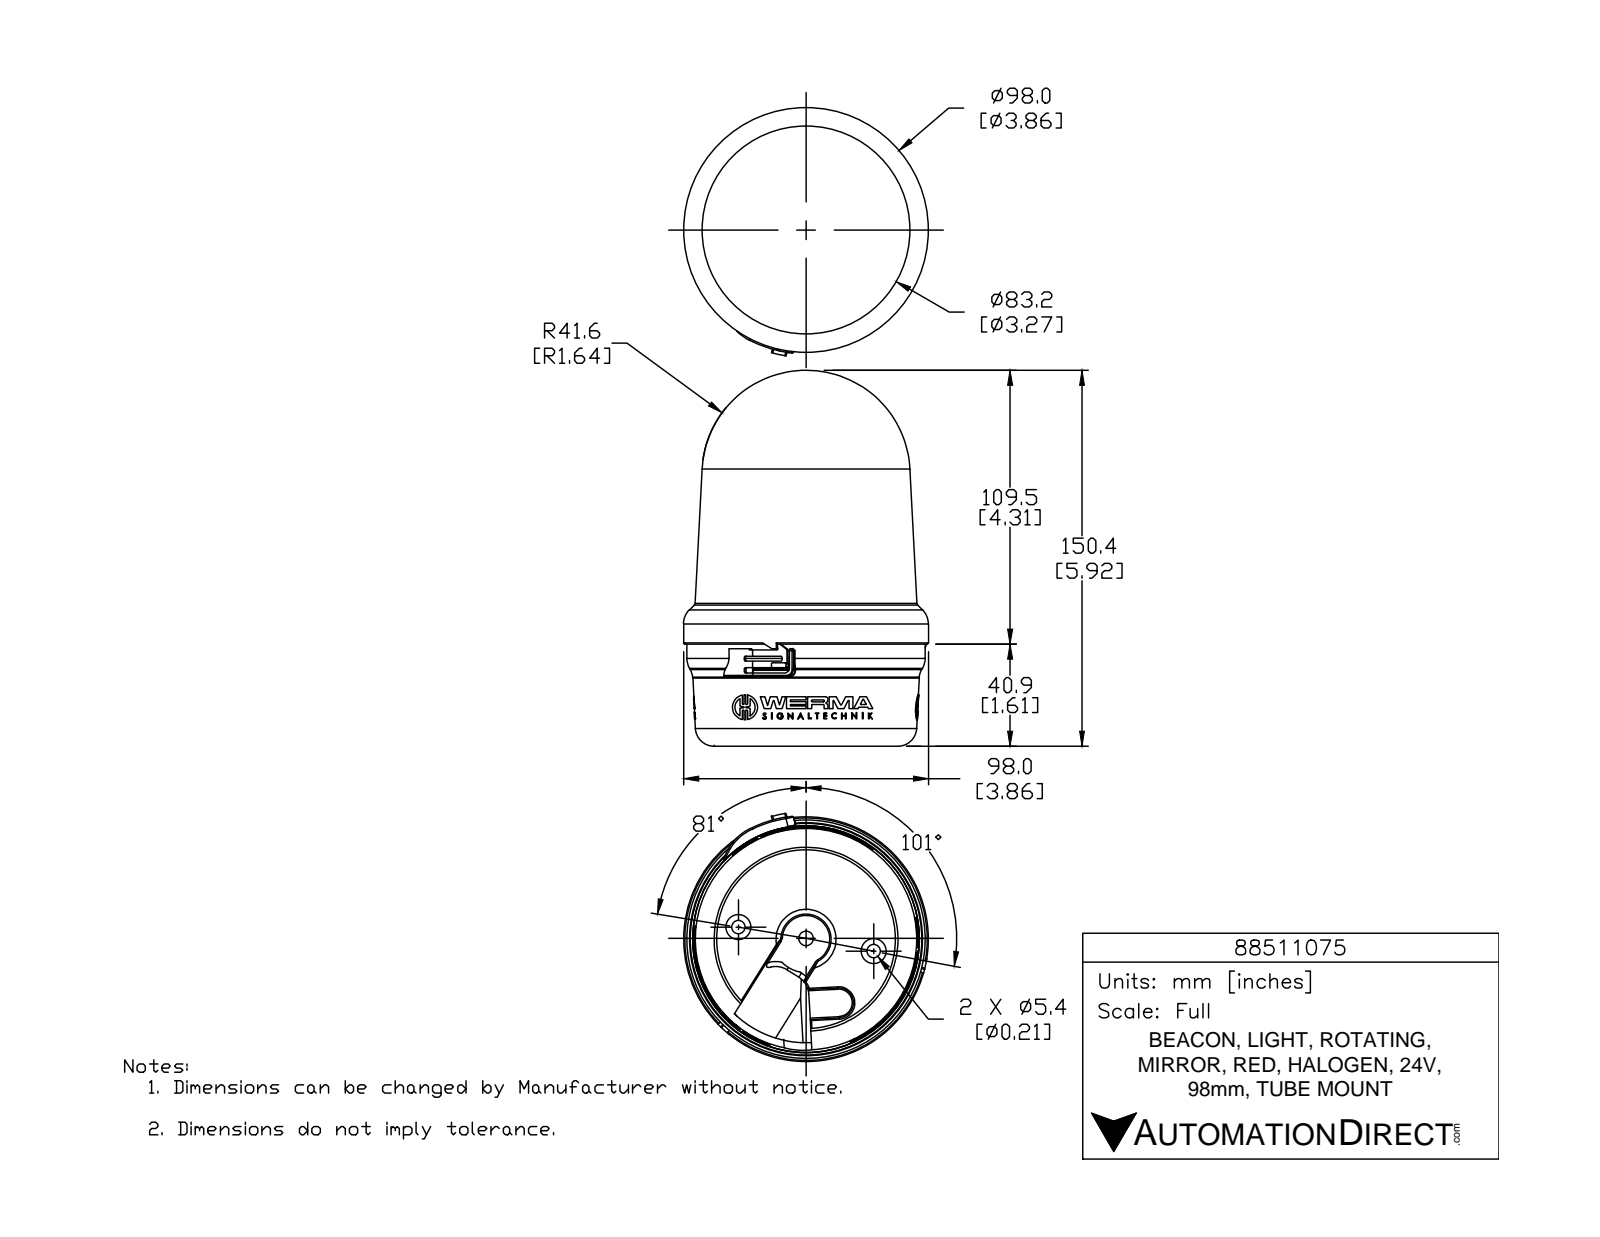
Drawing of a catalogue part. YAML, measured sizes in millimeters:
part_name: "88511075"
step_written_by: "SolidWorks 2015 (AUTOMOTIVE_DESIGN)"
units: millimeters
bodies: {solids: 1, faces: 1006, planar: 554, cylindrical: 189, other: 263}
overall_size: [201, 99.4, 98]
volume: 896400
surface_area: 58960
round_holes:
  - {diameter: 2, count: 3}
  - {diameter: 25.7, count: 1}
  - {diameter: 26, count: 1}
round_bosses_or_shafts:
  - {diameter: 11.5, count: 3}
  - {diameter: 2.9, count: 3}
  - {diameter: 98, count: 1}
  - {diameter: 35.8, count: 1}
  - {diameter: 32, count: 1}
partial_cylinders:
  - {radius: 0.5, count: 12}
  - {radius: 0.2, count: 9}
  - {radius: 0.2, count: 6}
  - {radius: 0.4, count: 6}
  - {radius: 0.4, count: 6}
  - {radius: 0.4, count: 6}
  - {radius: 6.7, count: 6}
  - {radius: 0.2, count: 3}
face_to_face_distances: [56.2, 11.7, 68, 8.5, 3.2, 64.7, 66.1, 62.9, 54.4, 1.9]
